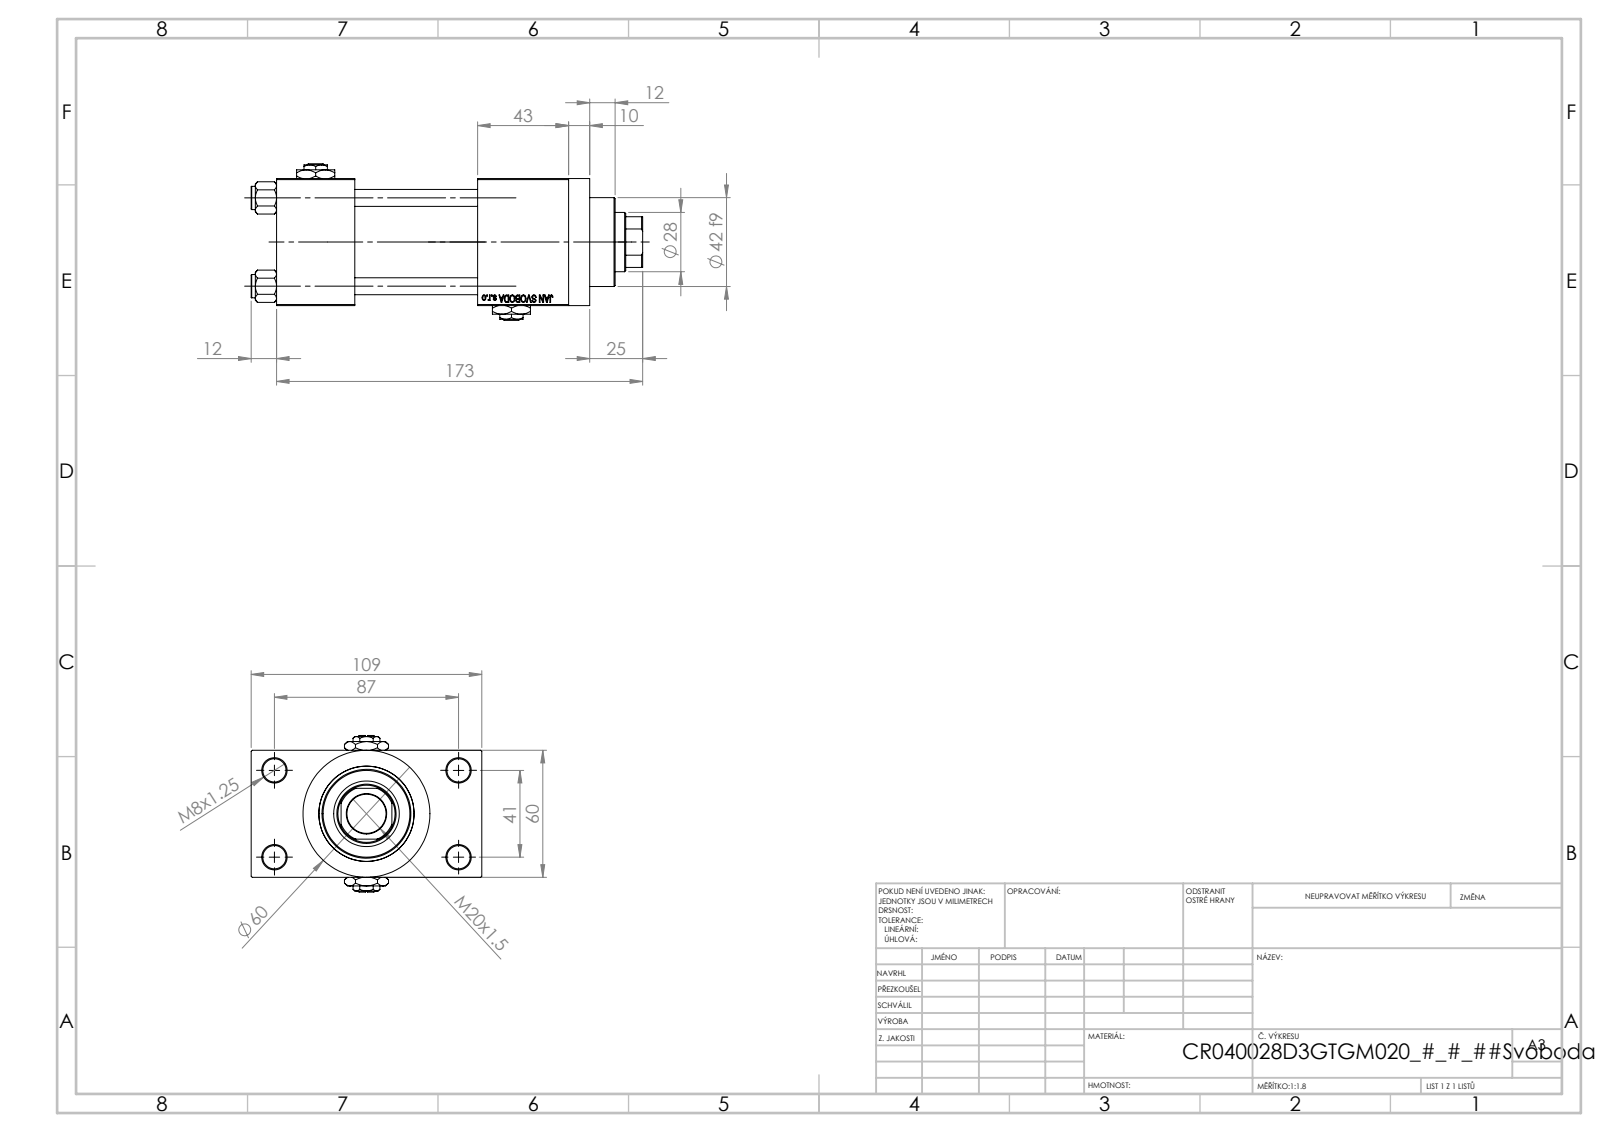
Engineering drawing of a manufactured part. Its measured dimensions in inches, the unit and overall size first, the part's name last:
Units: inches
Overall size (bounding box): 7.283 × 4.291 × 2.913
Round holes (diameter × count): ⌀0.315 ×4, ⌀0.433 ×4, ⌀0.276 ×2, ⌀0.656 ×2, ⌀0.945 ×2, ⌀0.728 ×1, ⌀1.102 ×1, ⌀1.22 ×1, ⌀1.575 ×1, ⌀1.772 ×1
Round bosses / shafts (diameter × count): ⌀0.433 ×4, ⌀2.362 ×1, ⌀1.811 ×1, ⌀1.654 ×1
Partial cylindrical surfaces — rounded edges, fillets, slot ends (radius × count): R0.531 ×1
Main face-to-face distances: 2.362, 3.327, 0.965, 2.283, 1.457, 3.74, 5.433, 3.976, 1.693, 4.291
Hole centre spacings: 0.892, 1.161, 1.642, 1.856, 1.893, 2.533, 3.011, 1.614
Volume: 32.77 in³ · Surface area: 200.9 in²
Bodies: 13 solids, 1189 faces (542 planar, 89 cylindrical, 558 other)
Part name (STEP PRODUCT): Zatka_pro_OIL_PORT; V215CR_VCP_D; V215_VC_A; V215CR_D_TYCINKA (+2 more)
STEP written by: SolidWorks 2019 (CONFIG_CONTROL_DESIGN)
